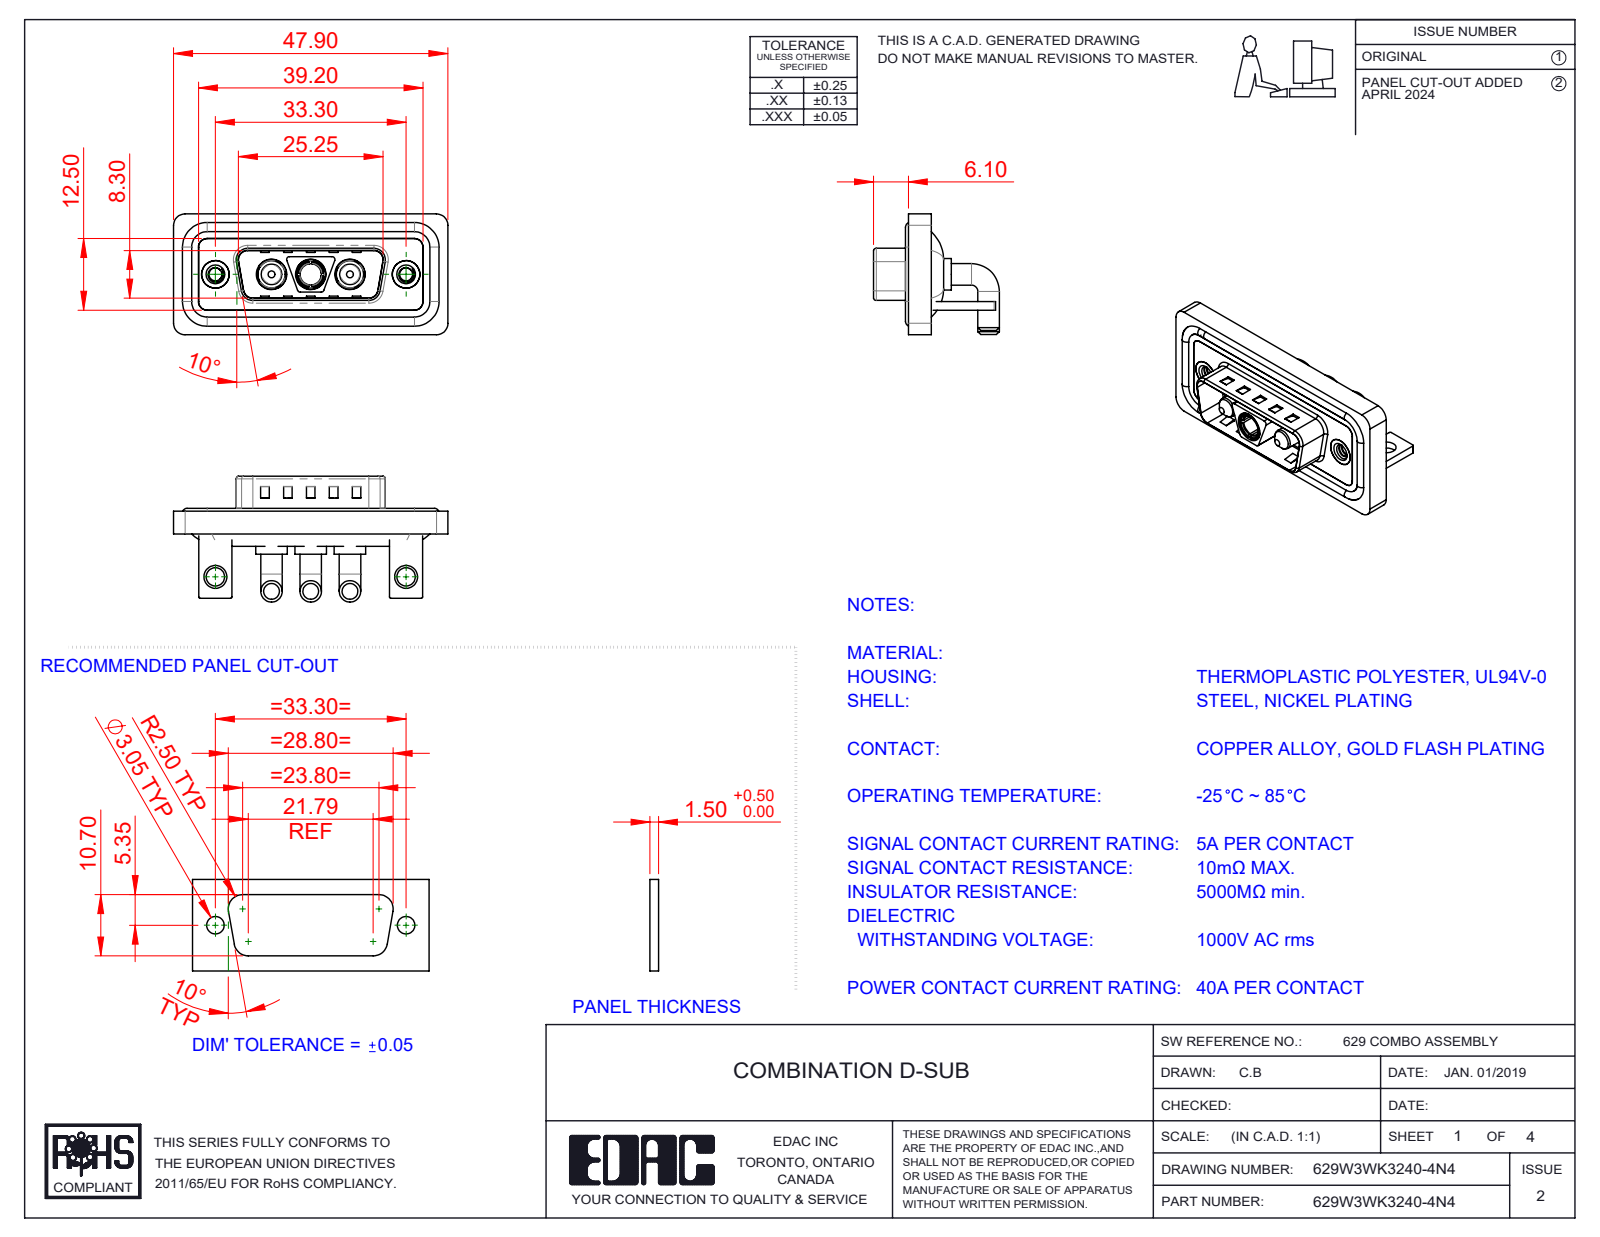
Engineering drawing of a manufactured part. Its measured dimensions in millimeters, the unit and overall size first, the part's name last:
Units: millimetres
Overall size (bounding box): 47.9 × 21.98 × 21.1
Round holes (diameter × count): ⌀4.85 ×3, ⌀5.3 ×3, ⌀2.26 ×2, ⌀3.2 ×2, ⌀4 ×2, ⌀4.8 ×2, ⌀5 ×2, ⌀3.7 ×1
Round bosses / shafts (diameter × count): ⌀3.75 ×6, ⌀1.6 ×4, ⌀5.5 ×3, ⌀5.2 ×3, ⌀4.75 ×3, ⌀4.9 ×2, ⌀3.6 ×2, ⌀4.96 ×1
Partial cylindrical surfaces — rounded edges, fillets, slot ends (radius × count): R2 ×21, R1.5 ×18, R0.25 ×16, R0.5 ×13, R1.6 ×8, R0.6 ×4, R0.65 ×4, R0.9 ×4
Main face-to-face distances: 0.4, 1.5, 0.8, 2.9, 1.1, 2.1, 3.7, 1.6, 1.2, 4.5
Hole centre spacings: 6.85, 9.8, 16.65, 23.5, 33.3, 13.7
Volume: 6 385 mm³ · Surface area: 10 136 mm²
Bodies: 15 solids, 661 faces (251 planar, 274 cylindrical, 136 other)
Part name (STEP PRODUCT): Power Pin_40A RA; 629W3WK3140-4N4; 629Combo Housing_3WK3; 629Combo Waterproof Housing_15 Contacts (+5 more)
STEP written by: SolidWorks 2023 (CONFIG_CONTROL_DESIGN)
